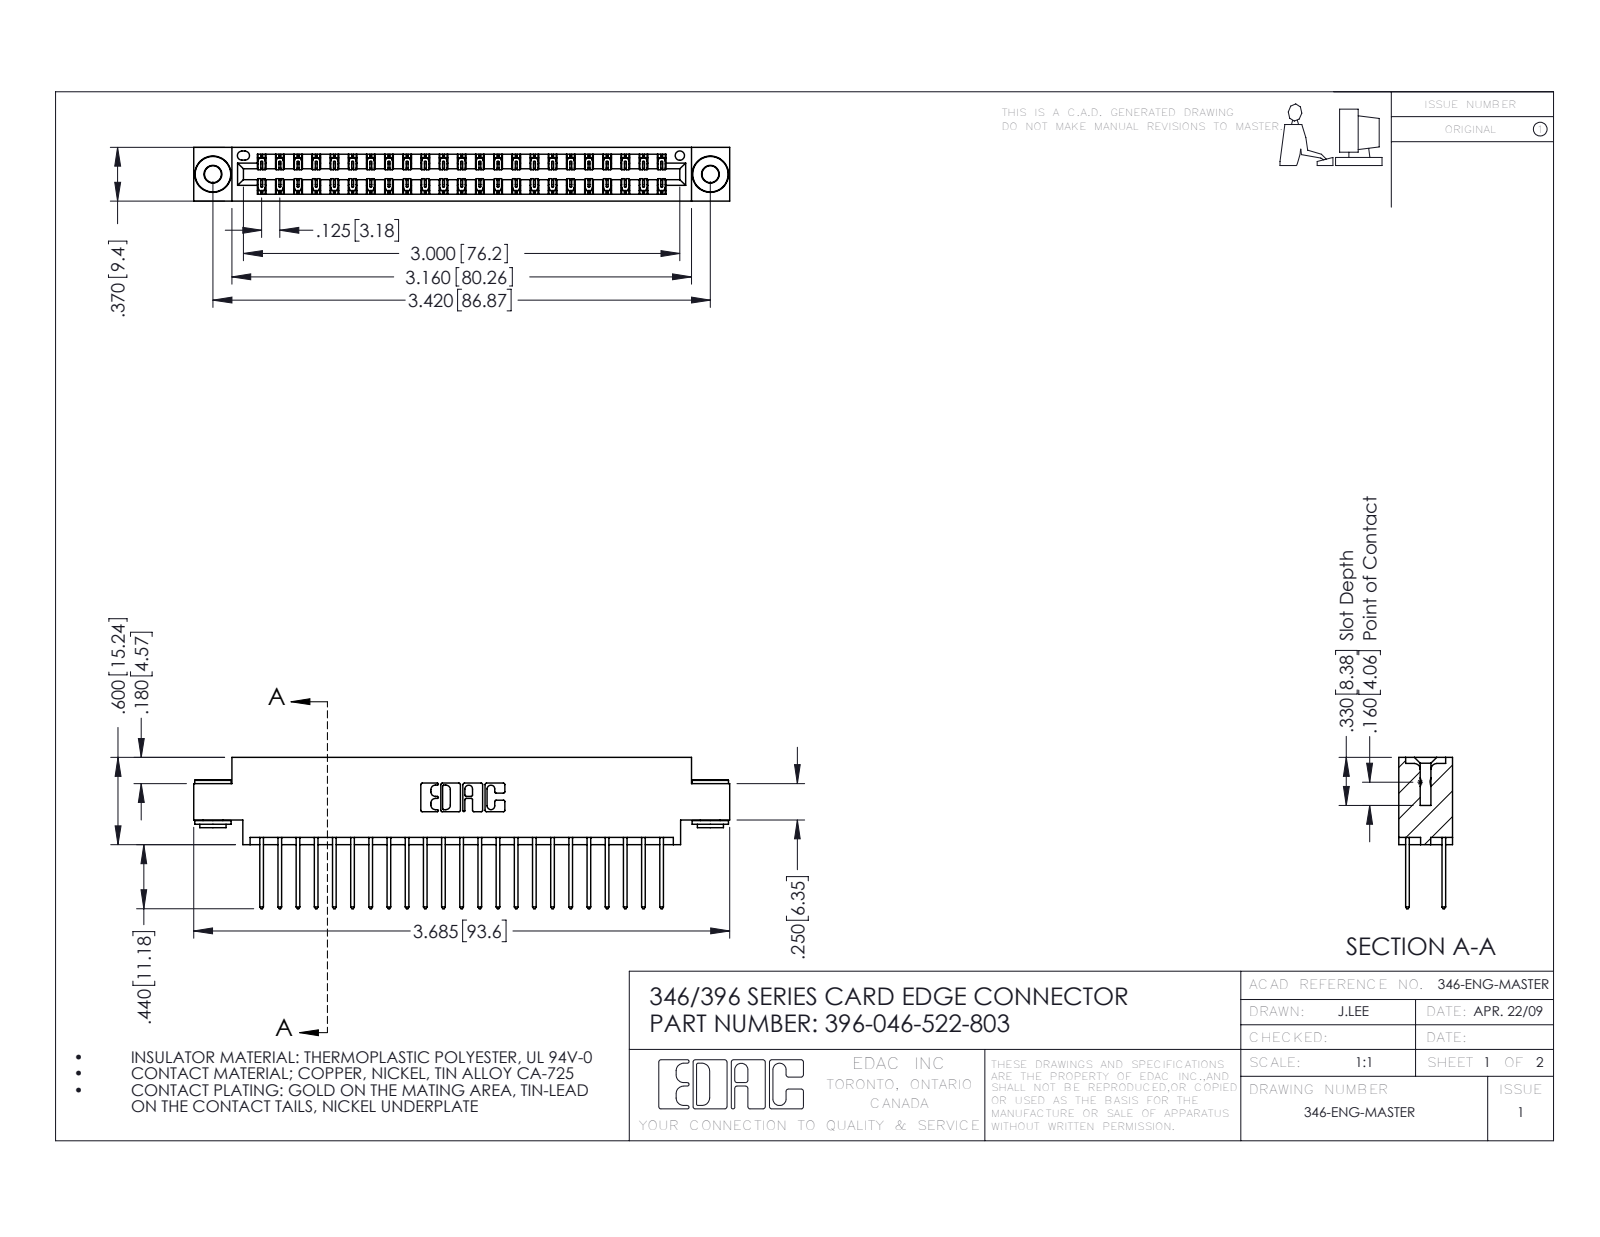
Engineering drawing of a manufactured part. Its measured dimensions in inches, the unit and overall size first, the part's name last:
Units: inches
Overall size (bounding box): 3.685 × 1.04 × 0.37
Round holes (diameter × count): ⌀0.116 ×2, ⌀0.156 ×2, ⌀0.064 ×1
Round bosses / shafts (diameter × count): ⌀0.25 ×2, ⌀0.18 ×2, ⌀0.136 ×2
Partial cylindrical surfaces — rounded edges, fillets, slot ends (radius × count): R0.006 ×69, R0.01 ×46, R0.01 ×22, R0.007 ×6, R0.031 ×6, R0.026 ×3, R0.014 ×2, R0.022 ×2
Main face-to-face distances: 0.048, 0.322, 0.25, 0.37, 0.025, 0.072, 0.298, 0.275, 0.148, 0.222
Hole centre spacings: 0.246, 3.212, 3.42
Volume: 0.547 in³ · Surface area: 20.09 in²
Bodies: 49 solids, 2556 faces (1700 planar, 848 cylindrical, 8 other)
Part name (STEP PRODUCT): 346 Part_0.170 Offset - 0.156 Dia-TH; 345-292-001_345-293-122; 345-250-002_345-250-002-102; 396-046-522-803
STEP written by: SolidWorks 2016 (CONFIG_CONTROL_DESIGN)
